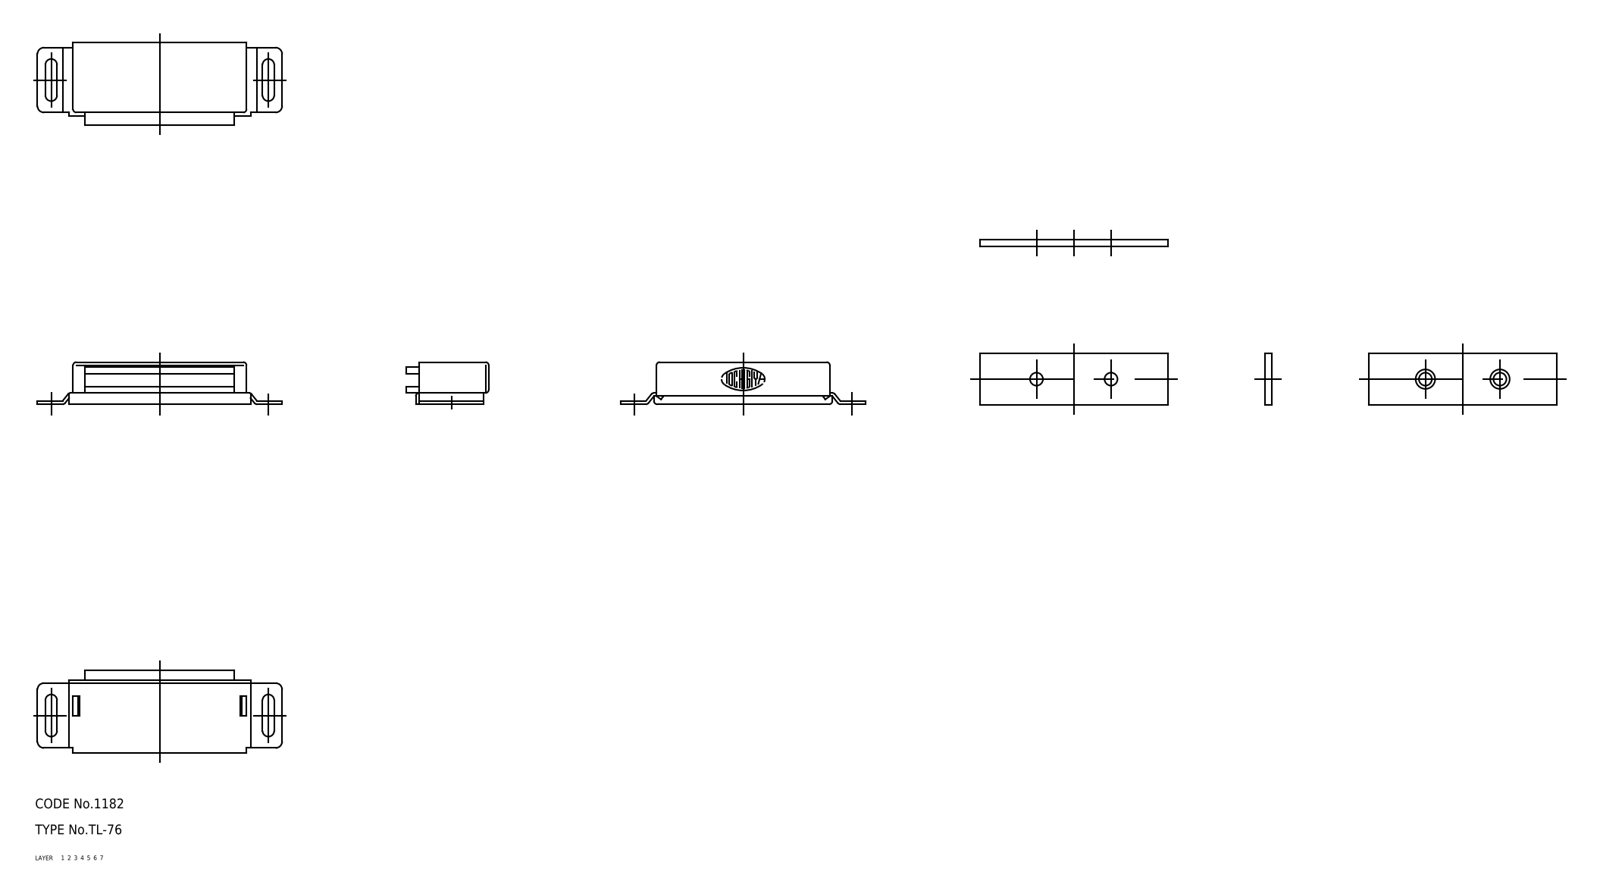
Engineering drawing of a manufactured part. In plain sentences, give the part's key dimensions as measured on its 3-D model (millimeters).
The part is named "67113235; 67113248; 67113261; 67113274 (+1 more)". Its 3-D file was written by "CADfix (AUTOMOTIVE_DESIGN)". It is 4 solids with 118 faces: 0 planar, 0 cylindrical and 118 other. Overall it measures 75.5 by 48 by 16 millimeters. Its volume is 6 005 cubic millimeters and its surface area 14 900 square millimeters.
